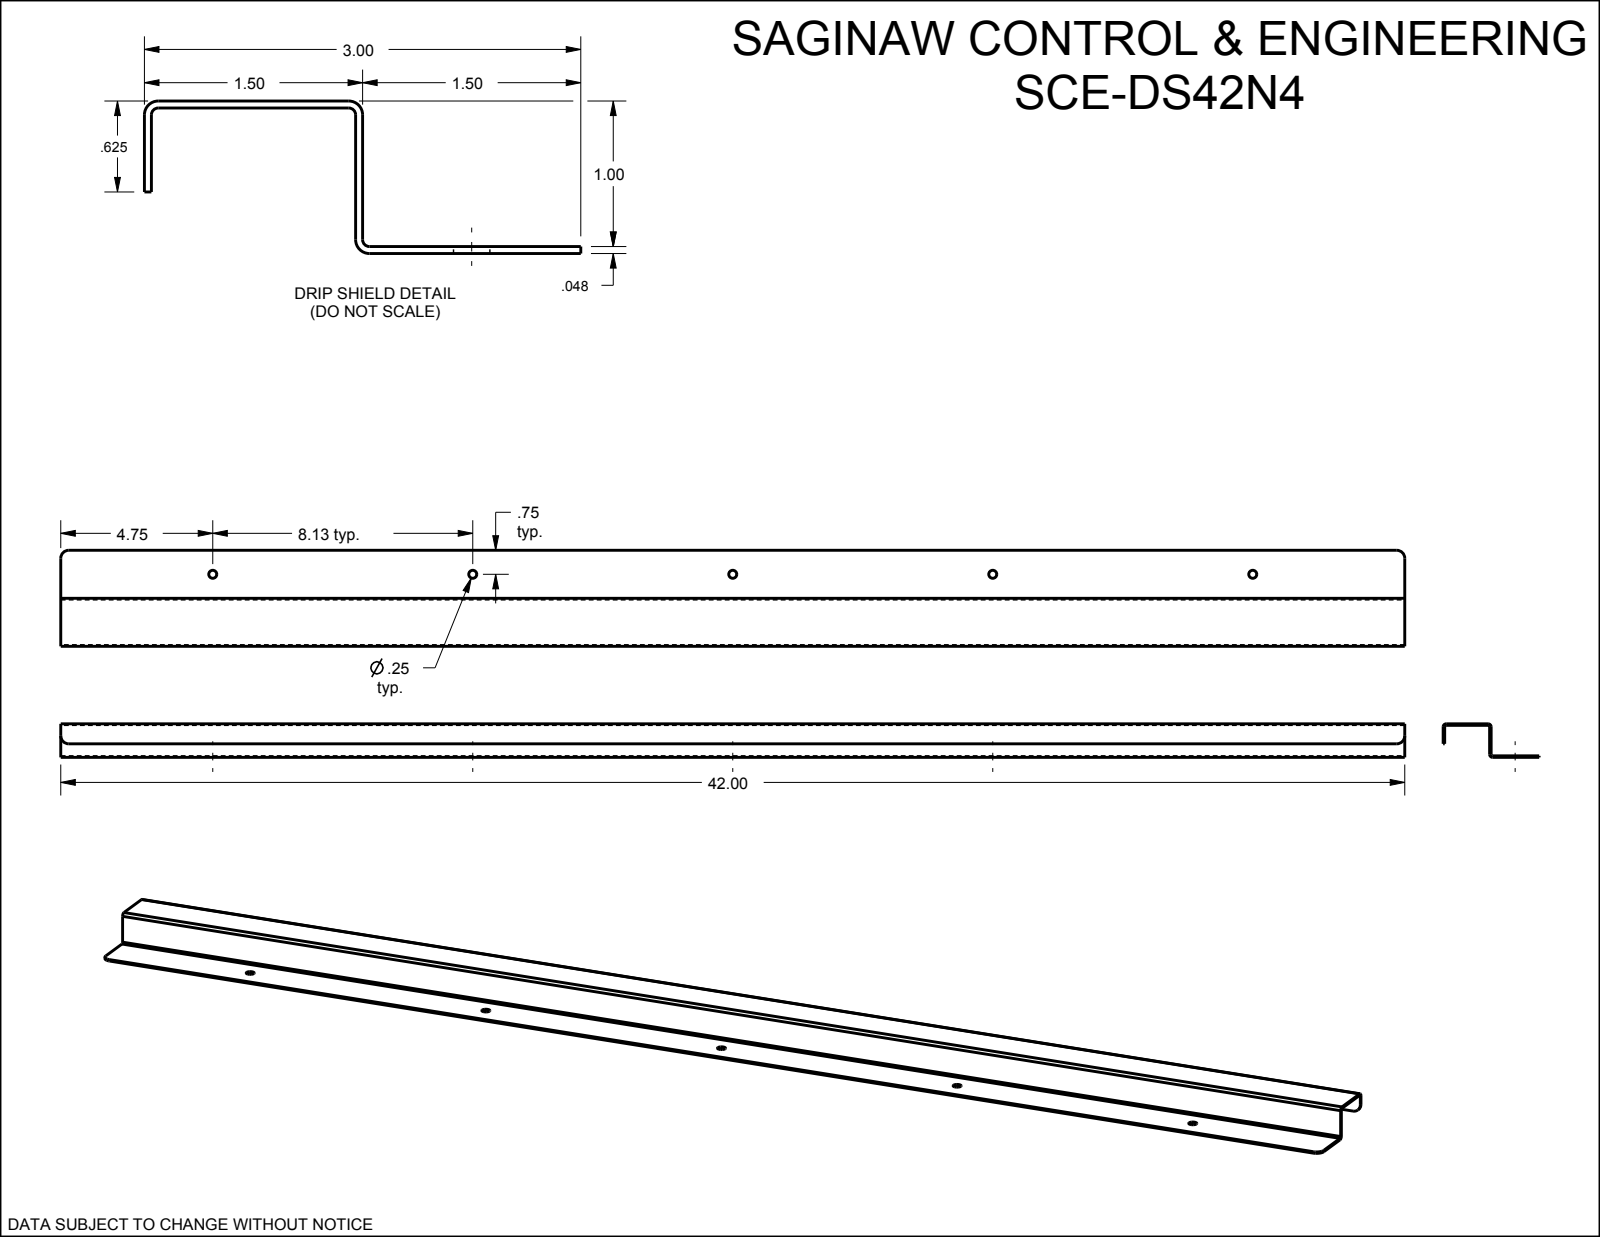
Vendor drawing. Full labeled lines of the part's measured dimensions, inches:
Part name (STEP PRODUCT): SCE-DS42N4
STEP written by: SolidWorks 2019 (CONFIG_CONTROL_DESIGN)
Units: inches
Bodies: 1 solid, 27 faces (12 planar, 15 cylindrical, 0 other)
Overall size (bounding box): 42 × 3 × 1.048
Volume: 9.029 in³ · Surface area: 380.8 in²
Round holes (diameter × count): ⌀0.25 ×5
Partial cylindrical surfaces — rounded edges, fillets, slot ends (radius × count): R0.25 ×4, R0.047 ×3, R0.095 ×3
Main face-to-face distances: 0.048, 1, 0.952, 1.048, 1.452, 1.5, 1.404, 0.423, 0.375, 0.577
Hole centre spacings: 8.125, 8.125, 16.25, 24.375, 16.25, 32.5
